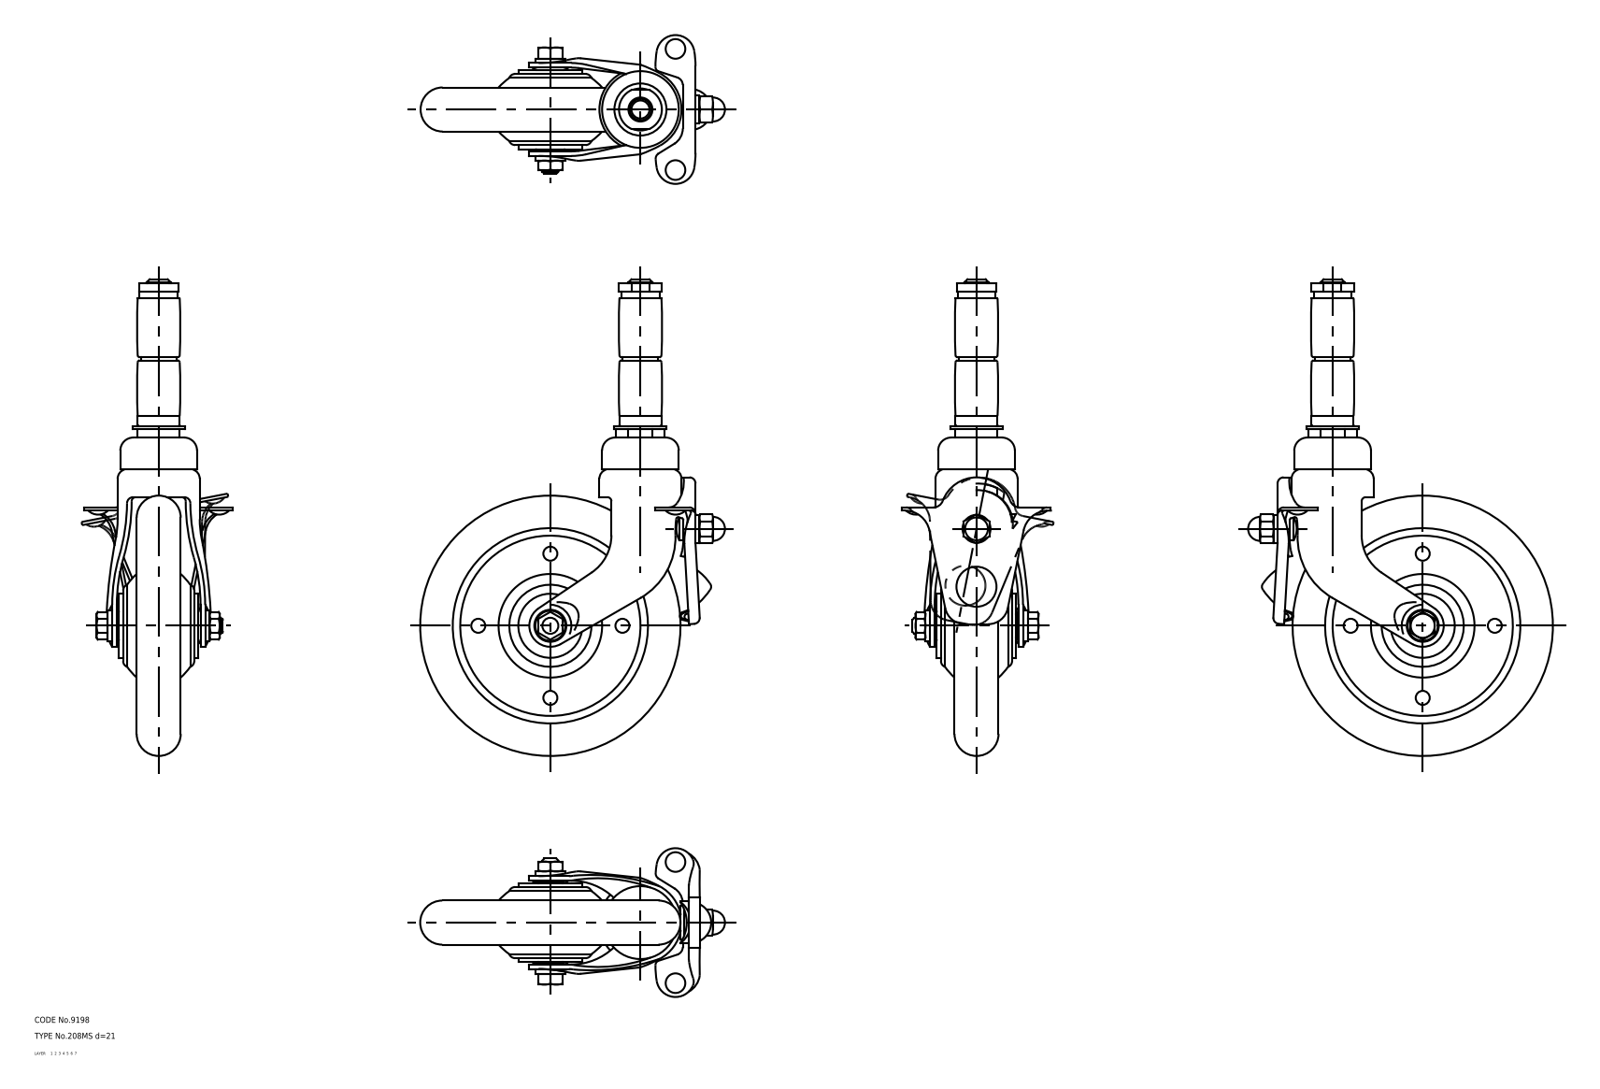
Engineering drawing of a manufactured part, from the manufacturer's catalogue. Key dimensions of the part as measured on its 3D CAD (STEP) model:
Part name (STEP PRODUCT): lever; wheel; main shaft; axle (+1 more)
STEP written by: CADfix (AUTOMOTIVE_DESIGN)
Units: millimetres
Bodies: 6 solids, 485 faces (0 planar, 0 cylindrical, 485 other)
Overall size (bounding box): 238 × 152.2 × 74.3
Volume: 309 865 mm³ · Surface area: 82 970 mm²
